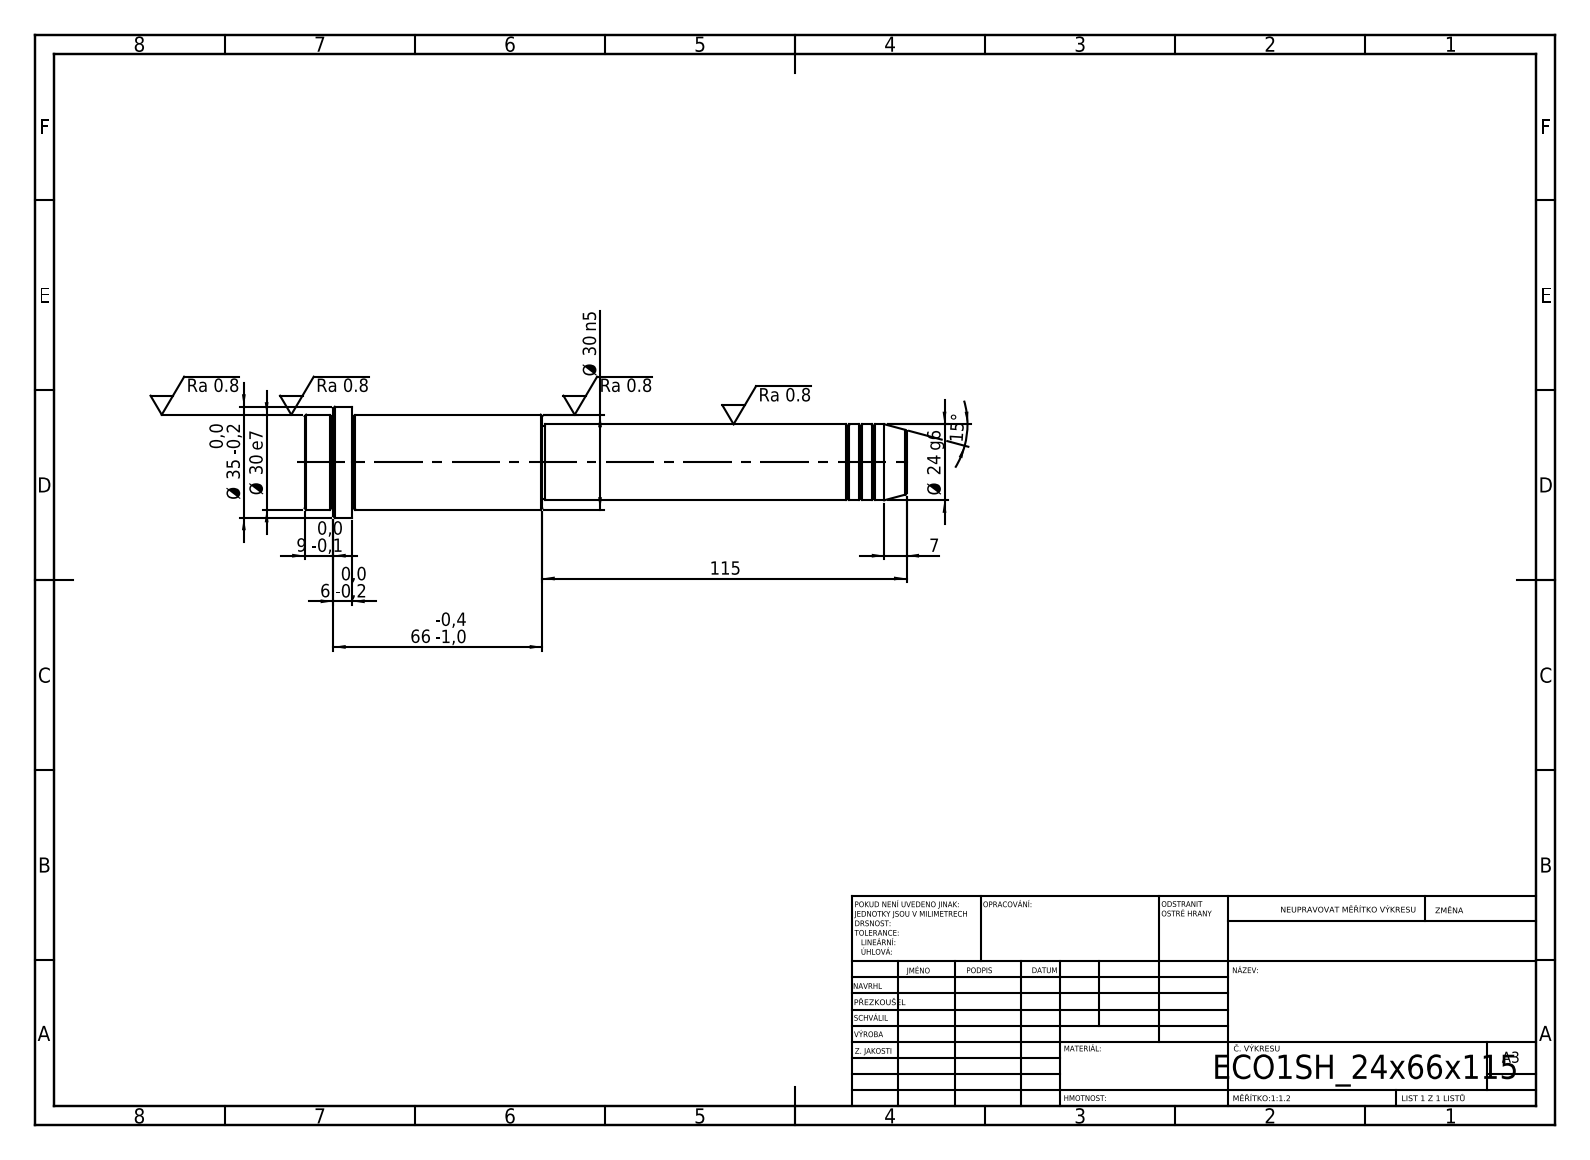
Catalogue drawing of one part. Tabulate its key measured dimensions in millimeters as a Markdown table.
| quantity | value |
| --- | --- |
| STEP written by | SolidWorks 2019 (CONFIG_CONTROL_DESIGN) |
| units | millimeters |
| bodies | 1 solid, 52 faces (6 planar, 16 cylindrical, 30 other) |
| overall size | 190 × 35 × 35 |
| volume | 105 866 mm³ |
| surface area | 17 799 mm² |
| round bosses / shafts (diameter × count) | 35 × 1, 30 × 1, 24 × 1, 23 × 1 |
| main face-to-face distances | 190, 175, 15, 115, 60, 75, 181, 66, 6, 9 |
